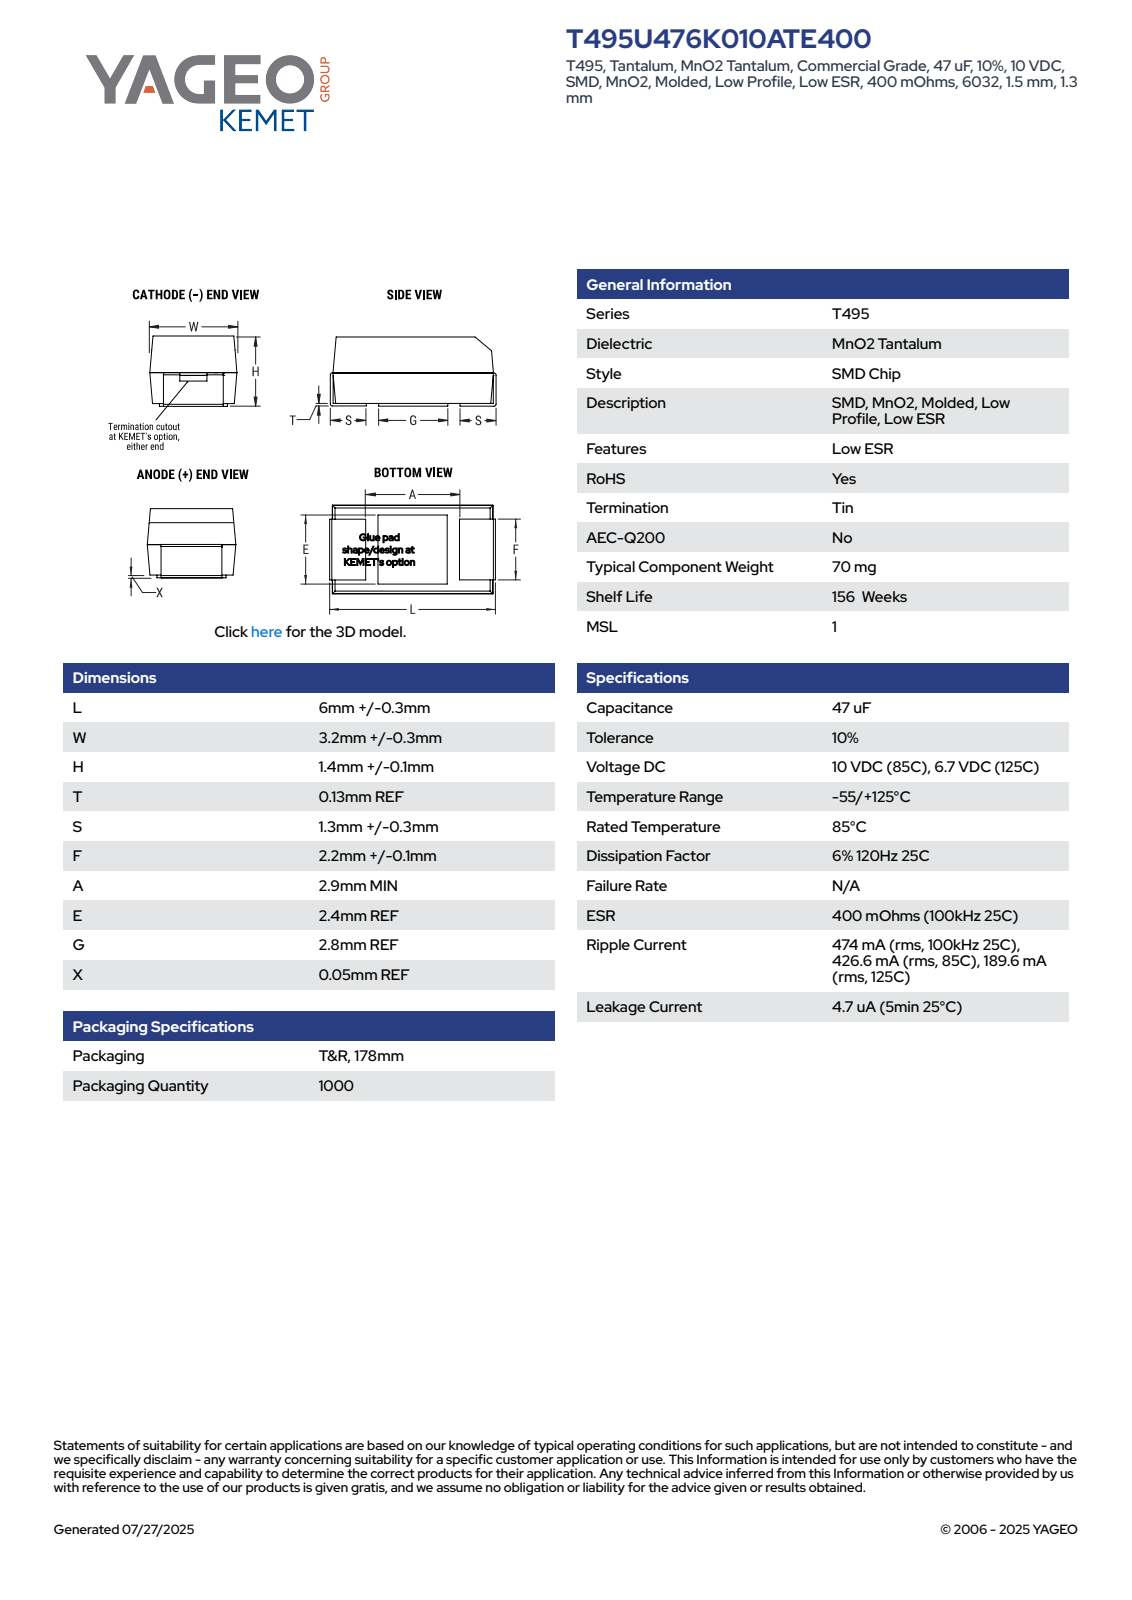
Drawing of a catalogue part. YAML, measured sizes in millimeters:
part_name: "CTSM_TCM2NBKRP_6032_L6.3W3.5H1.5T0.13S1.3F2.3A2.9E2.4G2.8X0.05"
step_written_by: "SolidWorks 2020 (AUTOMOTIVE_DESIGN)"
units: millimeters
bodies: {solids: 4, faces: 94, planar: 90, cylindrical: 4, other: 0}
overall_size: [6.3, 3.5, 1.5]
volume: 29
surface_area: 71
partial_cylinders:
  - {radius: 0.1, count: 4}
face_to_face_distances: [1.5, 3.38, 1.45, 6.17, 6.3, 6.04, 1.37, 2.3, 1.75, 4.55]
